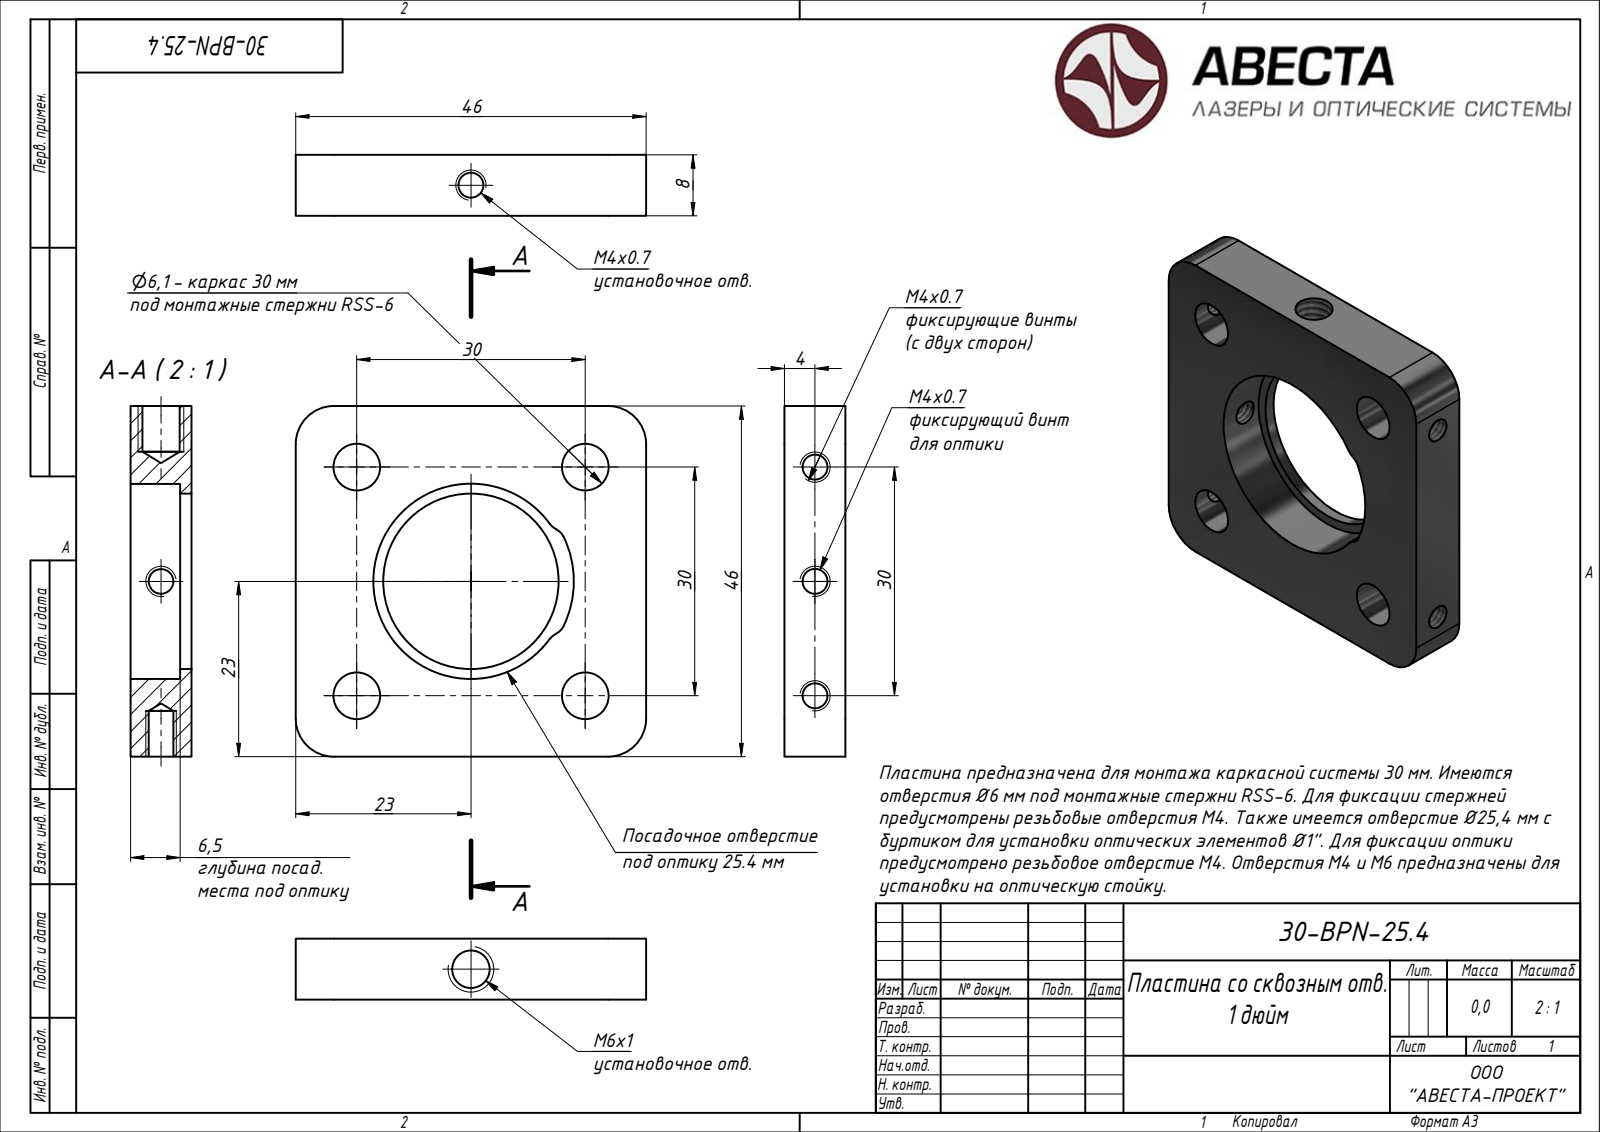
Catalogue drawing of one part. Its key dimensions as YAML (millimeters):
part_name: "30-BPN-25,4"
step_written_by: "Autodesk Inventor 2020 (AUTOMOTIVE_DESIGN)"
units: millimeters
bodies: {solids: 1, faces: 31, planar: 7, cylindrical: 22, other: 2}
overall_size: [46, 46, 8]
volume: 11360
surface_area: 6169
round_holes:
  - {diameter: 3.24, count: 4}
  - {diameter: 6.1, count: 4}
  - {diameter: 4.92, count: 1}
  - {diameter: 23, count: 1}
  - {diameter: 25.6, count: 1}
partial_cylinders:
  - {radius: 2, count: 4}
  - {radius: 5, count: 4}
  - {radius: 13.5, count: 1}
face_to_face_distances: [8, 46, 1.5, 6.5]
hole_center_spacings: [30, 21.21, 15, 42.43]
